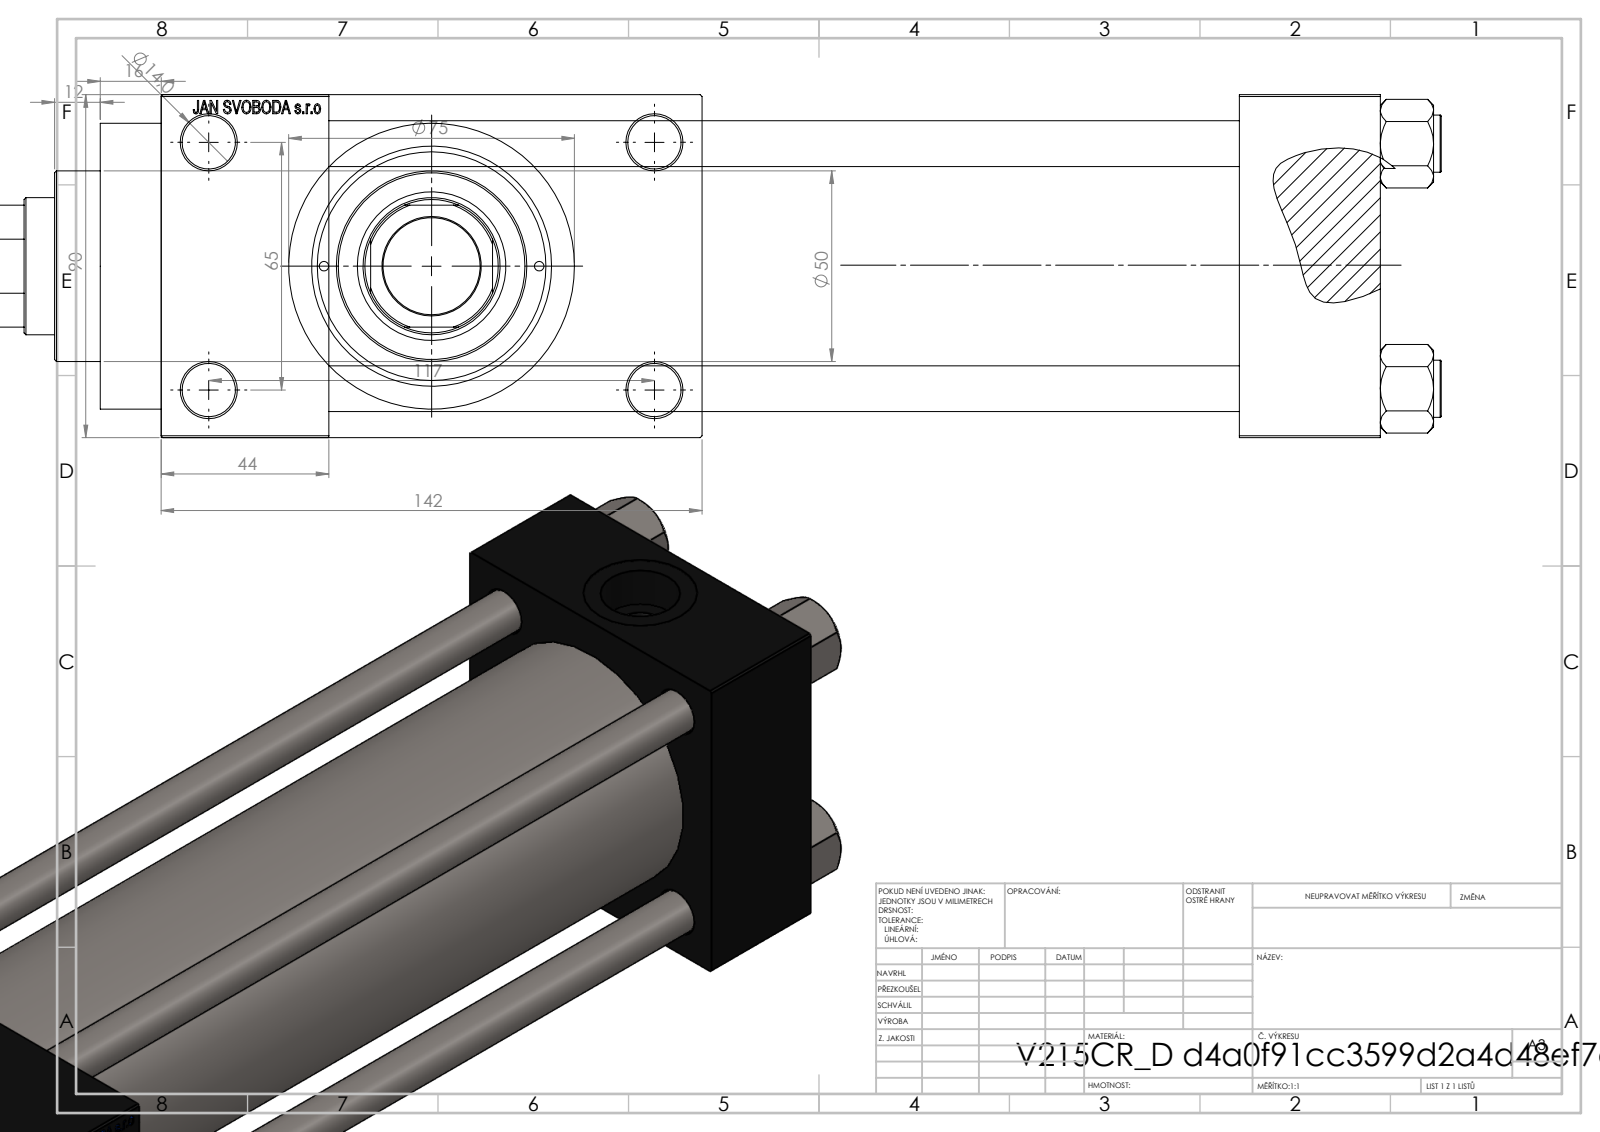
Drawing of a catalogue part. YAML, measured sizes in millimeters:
part_name: "NUT_M5_D; V215CR_VCP_D; V215CR_D_TYCINKA; V215CR_D_Body (+1 more)"
step_written_by: "SolidWorks 2019 (CONFIG_CONTROL_DESIGN)"
units: millimeters
bodies: {solids: 11, faces: 1112, planar: 499, cylindrical: 93, other: 520}
overall_size: [383, 142, 90]
volume: 1497000
surface_area: 326138
round_holes:
  - {diameter: 12, count: 4}
  - {diameter: 14, count: 4}
  - {diameter: 2.5, count: 2}
  - {diameter: 7, count: 2}
  - {diameter: 20.96, count: 2}
  - {diameter: 30, count: 2}
  - {diameter: 25.5, count: 1}
  - {diameter: 36, count: 1}
  - {diameter: 39, count: 1}
  - {diameter: 50, count: 1}
  - {diameter: 60, count: 1}
  - {diameter: 63, count: 1}
round_bosses_or_shafts:
  - {diameter: 15, count: 4}
  - {diameter: 75, count: 1}
  - {diameter: 69, count: 1}
partial_cylinders:
  - {radius: 17.5, count: 1}
face_to_face_distances: [90, 239, 37, 276, 320, 283, 44, 26, 116, 142]
hole_center_spacings: [26.35, 32.39, 44.4, 45.47, 64.3, 66.92, 68.42, 69.81]
